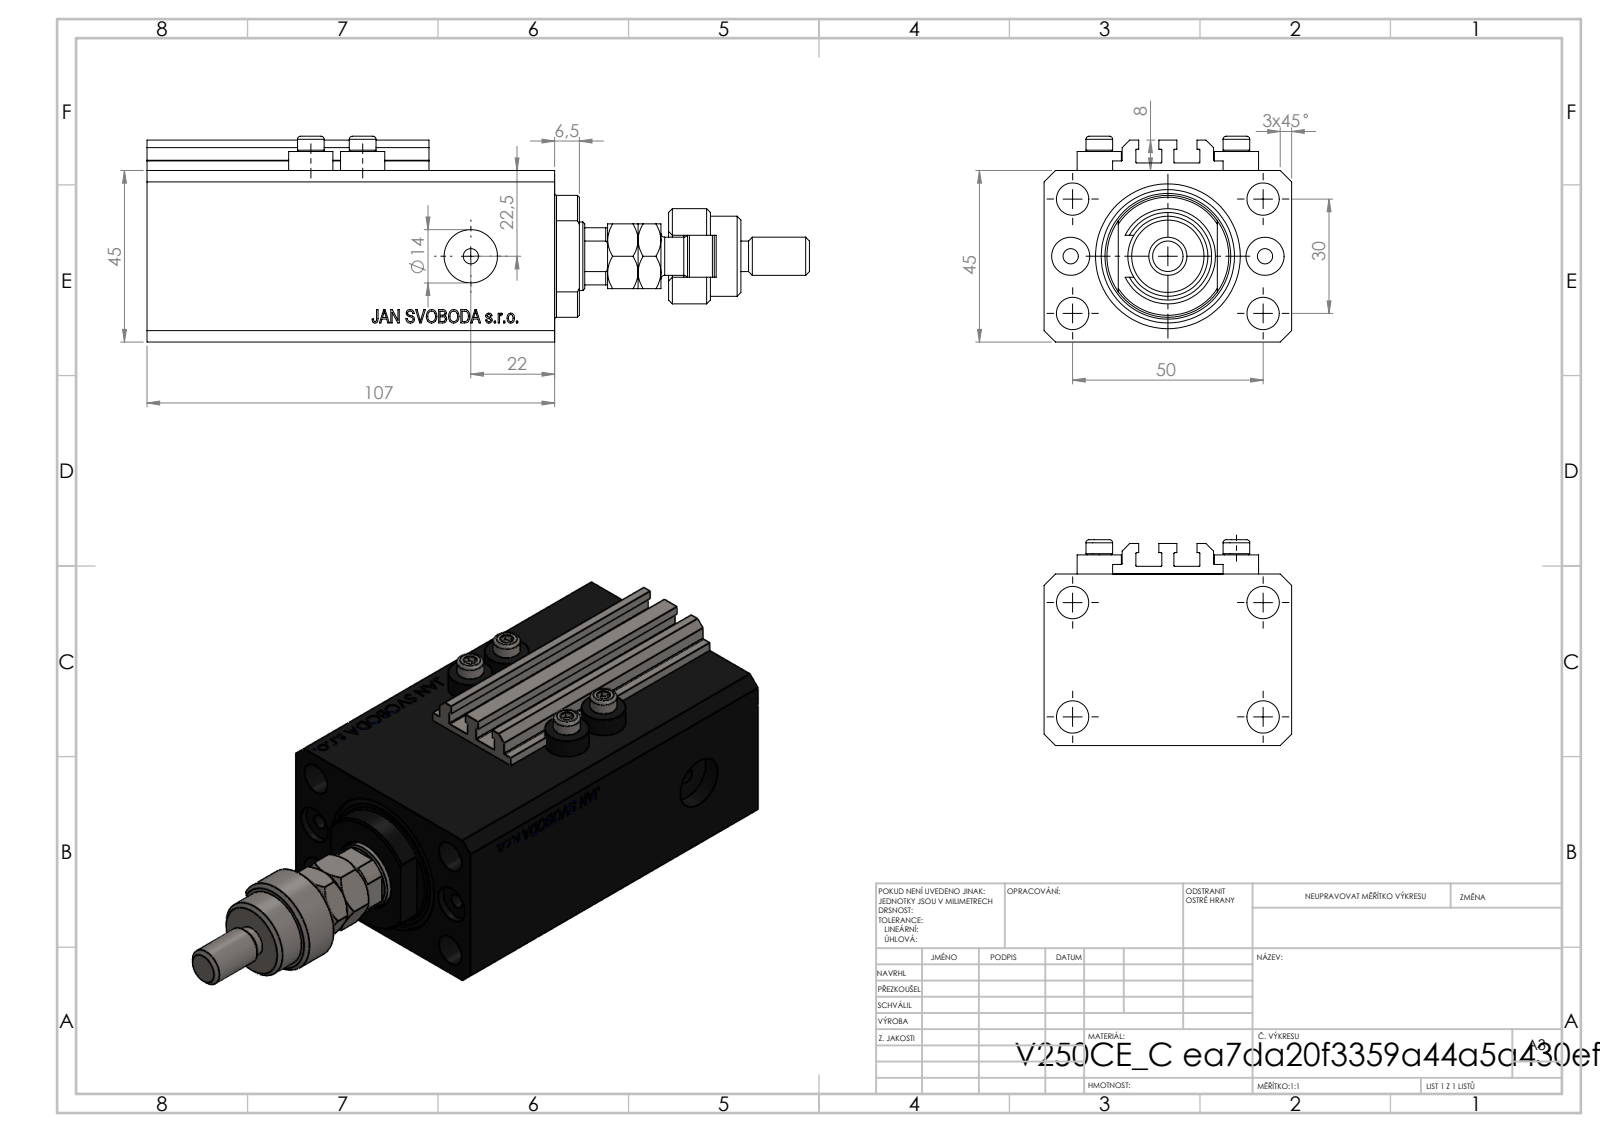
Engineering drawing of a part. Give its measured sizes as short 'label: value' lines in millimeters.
name: V250CE_C_VCP; MFA; FEMALE_PART_FOR_DFA; V250CE_C_Body (+2 more)
written by: SolidWorks 2019 (CONFIG_CONTROL_DESIGN)
unit: mm
bodies: 10 solids, 1118 faces (531 planar, 99 cylindrical, 488 other)
size: 173.9 × 65 × 54
volume: 300 777 mm³; area: 81 539 mm²
holes: 8× ⌀4, 5× ⌀8.5, 2× ⌀10, 2× ⌀14, 1× ⌀18, 1× ⌀38
bosses: 4× ⌀11.6, 4× ⌀7, 1× ⌀25, 1× ⌀21, 1× ⌀16, 1× ⌀10, 1× ⌀8
rounds: 10× R0.2, 1× R5.5, 1× R8.5, 1× R8.75, 1× R16
face distances: 45, 65, 81.9, 107, 25.1, 47, 2, 3, 2.5, 10
hole spacings: 15.01, 29.15, 52.68, 13.6, 25.5, 30, 36, 38.48
